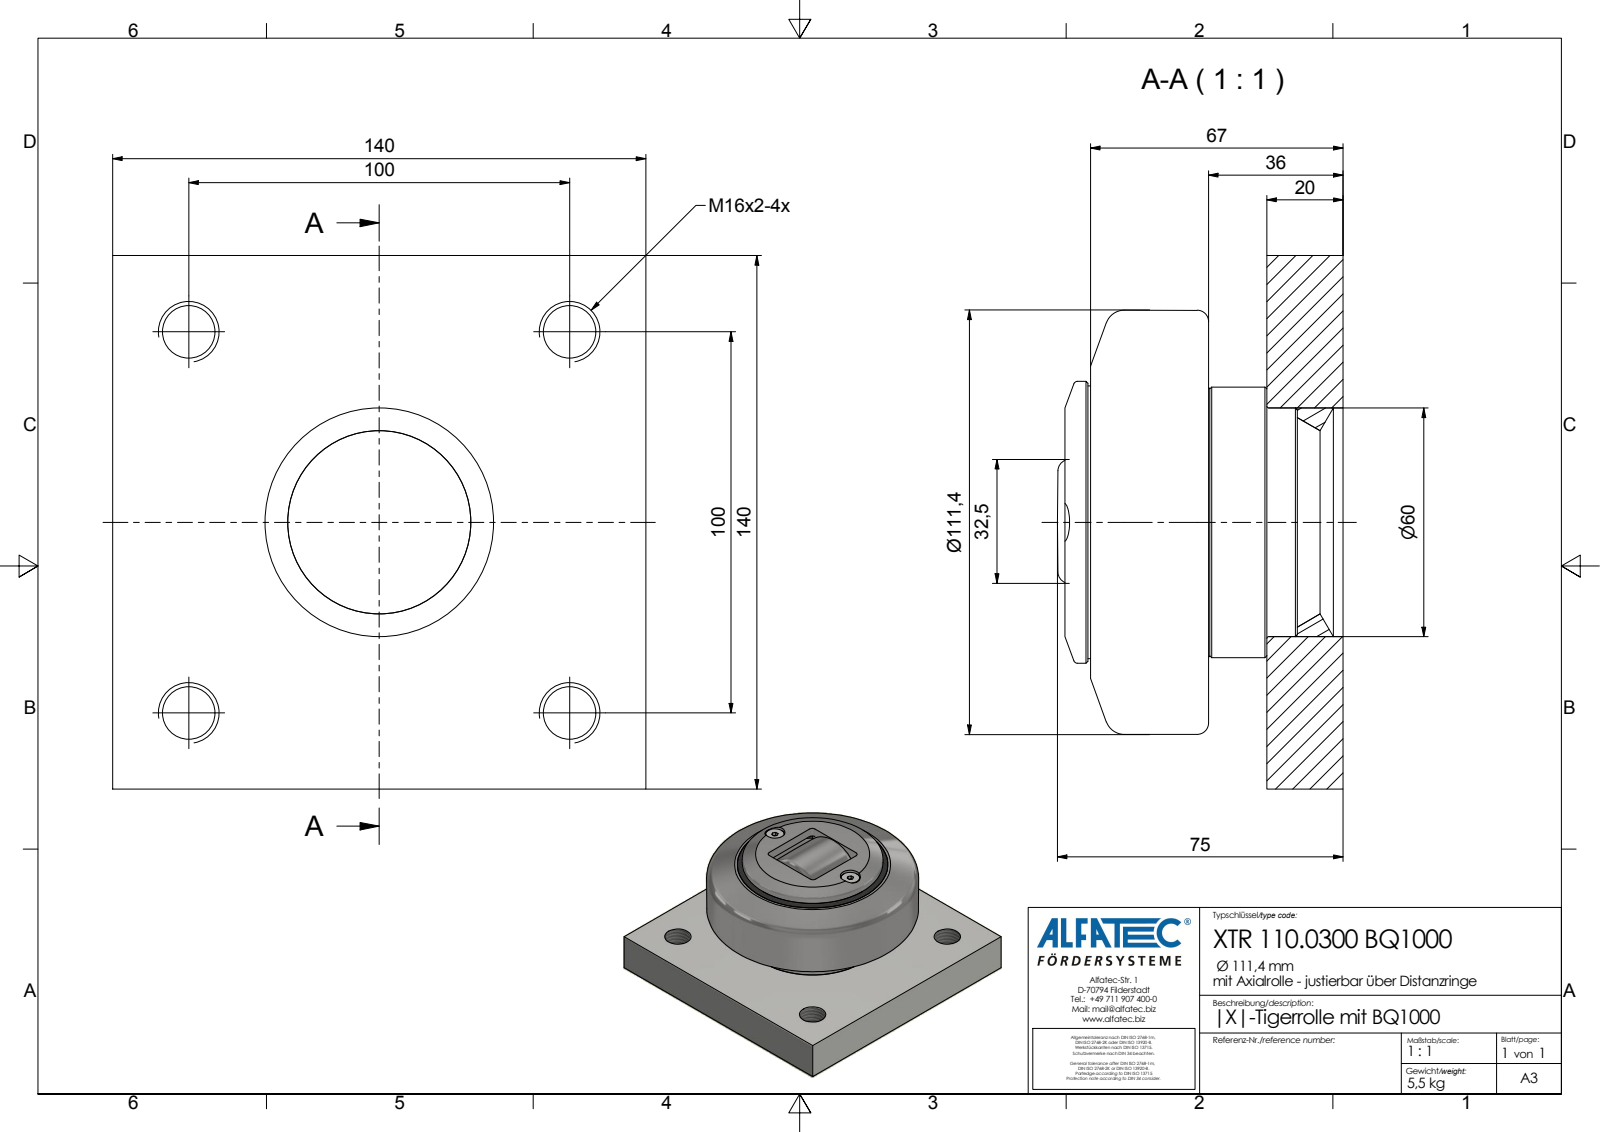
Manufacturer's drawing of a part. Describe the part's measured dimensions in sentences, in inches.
The part is named "XTR 110.0300 BQ1000_Kontur". Its 3-D file was written by "Autodesk Inventor 2020 (AUTOMOTIVE_DESIGN)". It is 2 solids with 127 faces: 52 planar, 46 cylindrical and 29 other. Overall it measures 5.512 by 5.512 by 2.953 inches. Its volume is 41.19 cubic inches and its surface area 183.9 square inches. Round holes: 4 of diameter 0.545, 2 of diameter 0.217, 2 of diameter 0.413, 1 of diameter 0.118, 1 of diameter 1.024, 1 of diameter 1.102, 1 of diameter 2.362, 1 of diameter 2.5, 1 of diameter 3.071, 1 of diameter 3.11, 1 of diameter 3.28. Round bosses or shafts: 2 of diameter 0.384, 2 of diameter 0.197, 1 of diameter 3.031, 1 of diameter 2.913, 1 of diameter 2.819, 1 of diameter 2.795, 1 of diameter 2.776, 1 of diameter 2.728. Partial cylindrical surfaces (rounded edges, fillets, slot ends): 4 of radius 0.079, 1 of radius 0.748. The main face-to-face distances are 0.787, 5.512, 1.39, 0.236, 0.602, 2.087, 2.638, 0.02, 0.276, 1.154. The hole center spacings are 2.151, 2.784, 3.648, 3.937, 1.102, 5.568, 0.256, 2.205.
